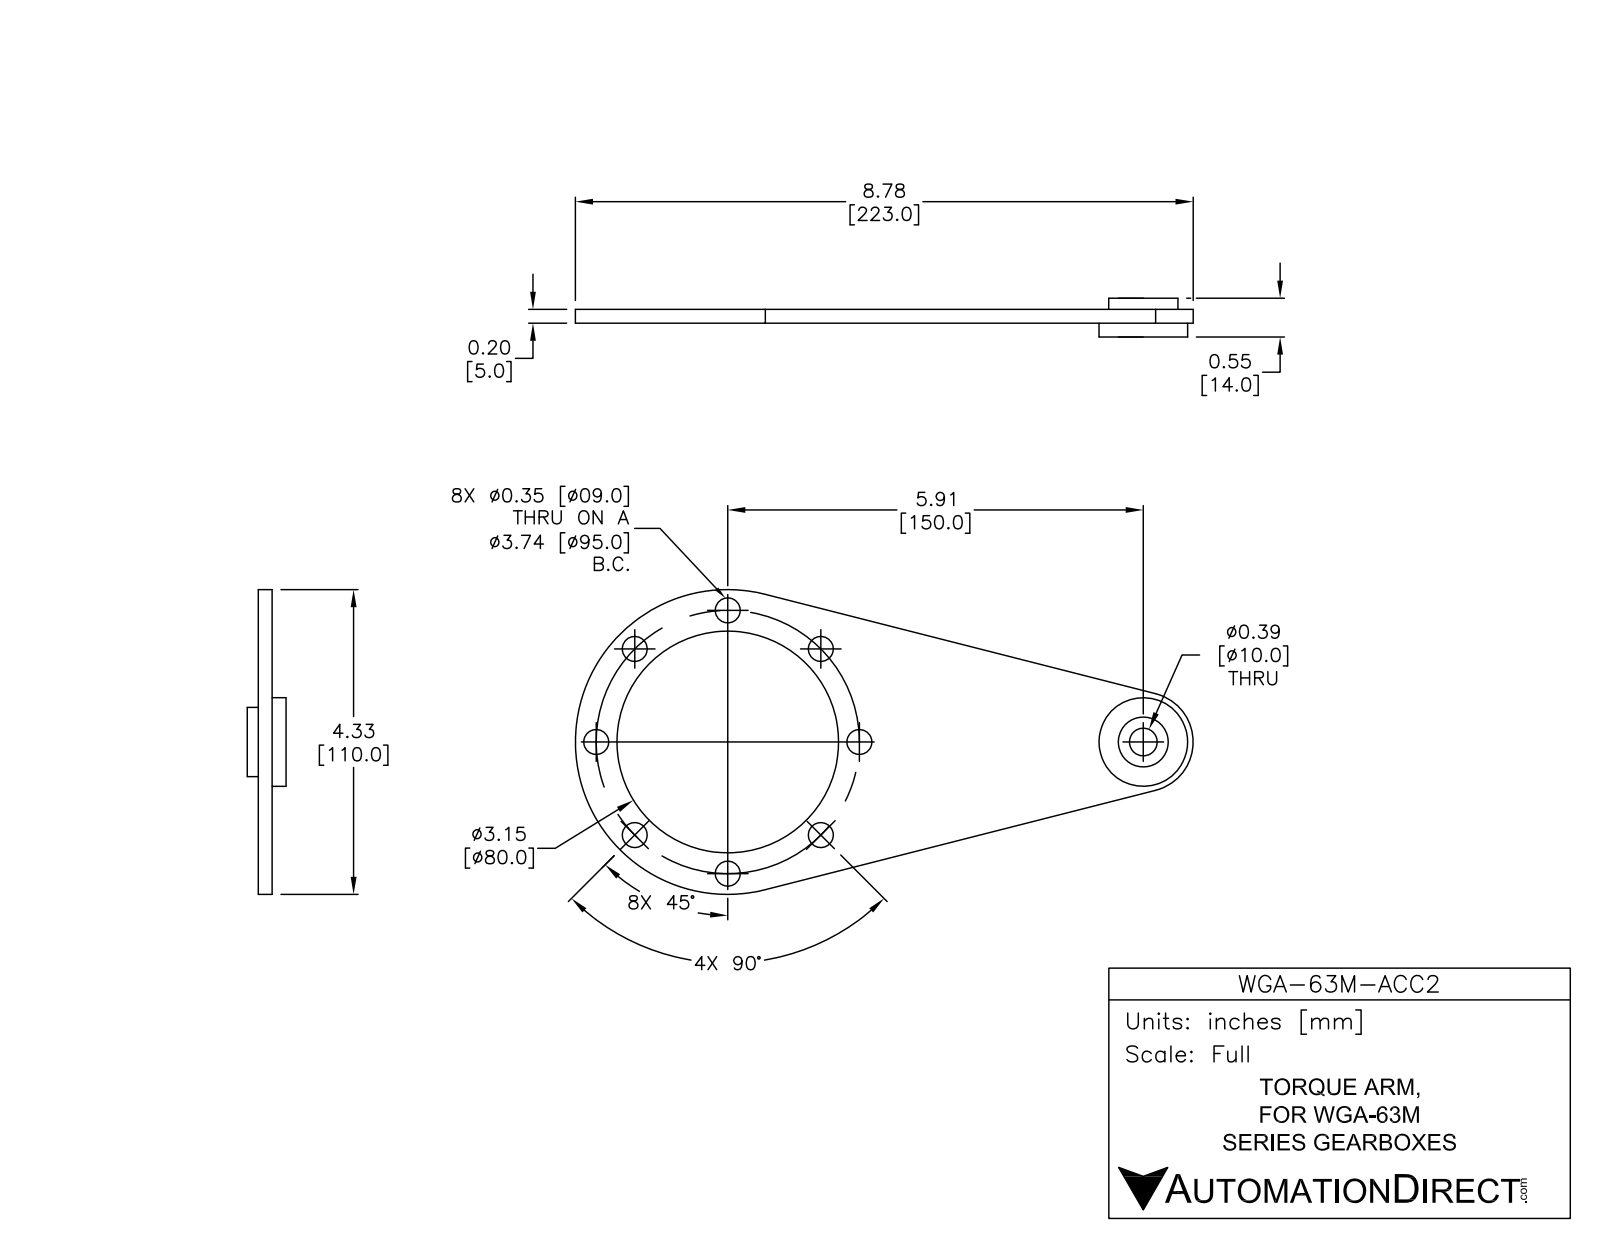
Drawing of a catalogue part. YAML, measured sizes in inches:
part_name: "WGA-63M-ACC2"
step_written_by: "SolidWorks 2014 (AUTOMOTIVE_DESIGN)"
units: inches
bodies: {solids: 4, faces: 46, planar: 10, cylindrical: 36, other: 0}
overall_size: [8.78, 4.331, 0.551]
volume: 3.657
surface_area: 48.6
round_holes:
  - {diameter: 0.354, count: 8}
  - {diameter: 0.394, count: 1}
  - {diameter: 0.709, count: 1}
  - {diameter: 3.15, count: 1}
round_bosses_or_shafts:
  - {diameter: 1.26, count: 1}
  - {diameter: 0.984, count: 1}
partial_cylinders:
  - {radius: 0.709, count: 1}
  - {radius: 2.165, count: 1}
face_to_face_distances: [0.197, 0.394, 0.157, 0.354, 0.551]
hole_center_spacings: [1.431, 1.87, 2.645, 3.456, 3.74, 3.741, 4.77, 6.194]
